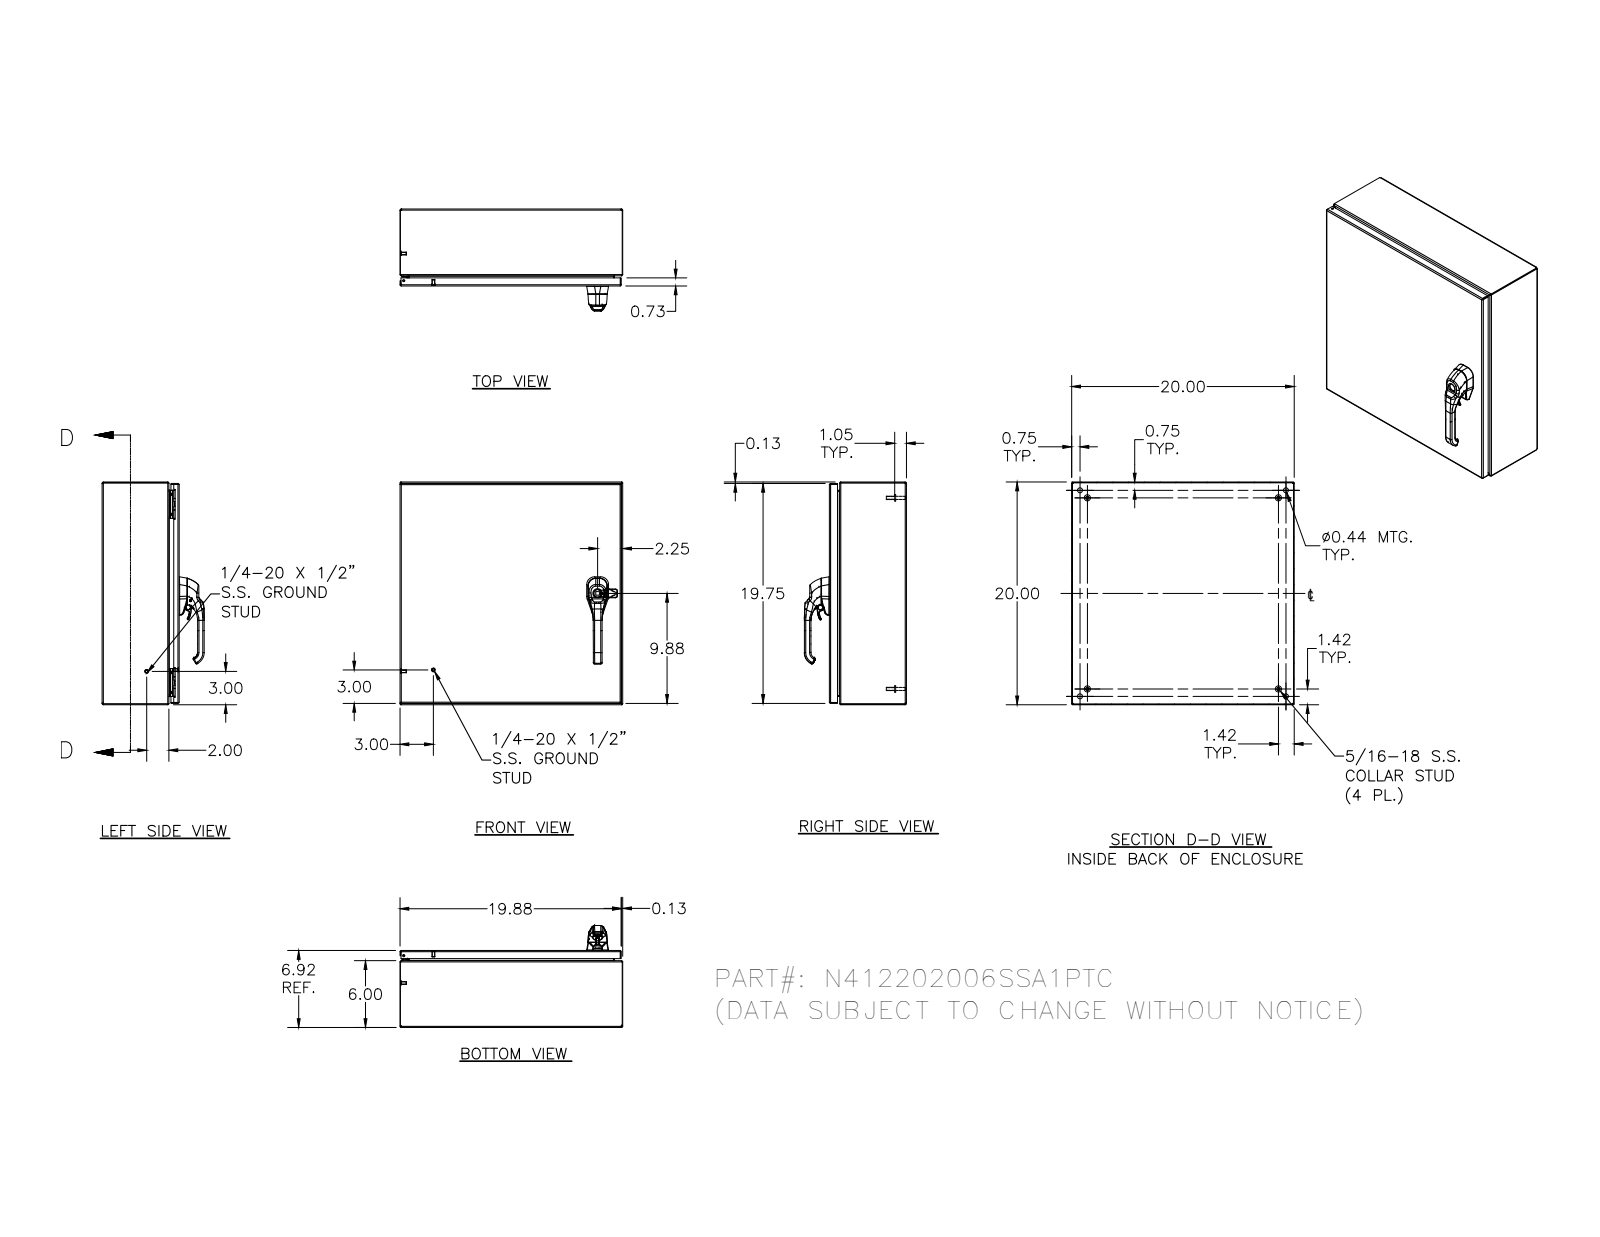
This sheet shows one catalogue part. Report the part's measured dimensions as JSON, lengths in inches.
{"part_name": "N412202006SSA1PTC; N412202006SSA1PTCBKP; N4122020SSA1PTCLID; HFW328176 (+8 more)", "step_written_by": "Autodesk Inventor 2012 (AUTOMOTIVE_DESIGN)", "units": "inches", "bodies": {"solids": 41, "faces": 2784, "planar": 882, "cylindrical": 1037, "other": 865}, "overall_size": [20, 20, 9.166], "volume_in3": 113.8, "surface_area_in2": 2995, "round_holes": [[0.188, 5], [0.093, 4], [0.152, 4], [0.167, 4], [0.172, 4], [0.437, 4], [0.213, 3], [0.281, 3], [0.156, 2], [0.315, 2], [0.402, 2], [0.413, 2]], "round_bosses_or_shafts": [[0.25, 10], [0.563, 4], [0.36, 4], [0.32, 4], [0.3, 4], [0.275, 4], [0.256, 4], [0.164, 4]], "partial_cylinders_radius": [[0.02, 174], [0.012, 101], [0.031, 30], [0.05, 26], [0.019, 21], [0.105, 20], [0.016, 18], [0.079, 14]], "face_to_face_distances": [0.074, 6.843, 19.926, 6.917, 6.769, 19.852, 20, 5.926, 0.917, 0.739], "hole_center_spacings": [15.996, 18.5, 18.872, 0.017, 0.66, 16.004, 16.656, 0.019]}
